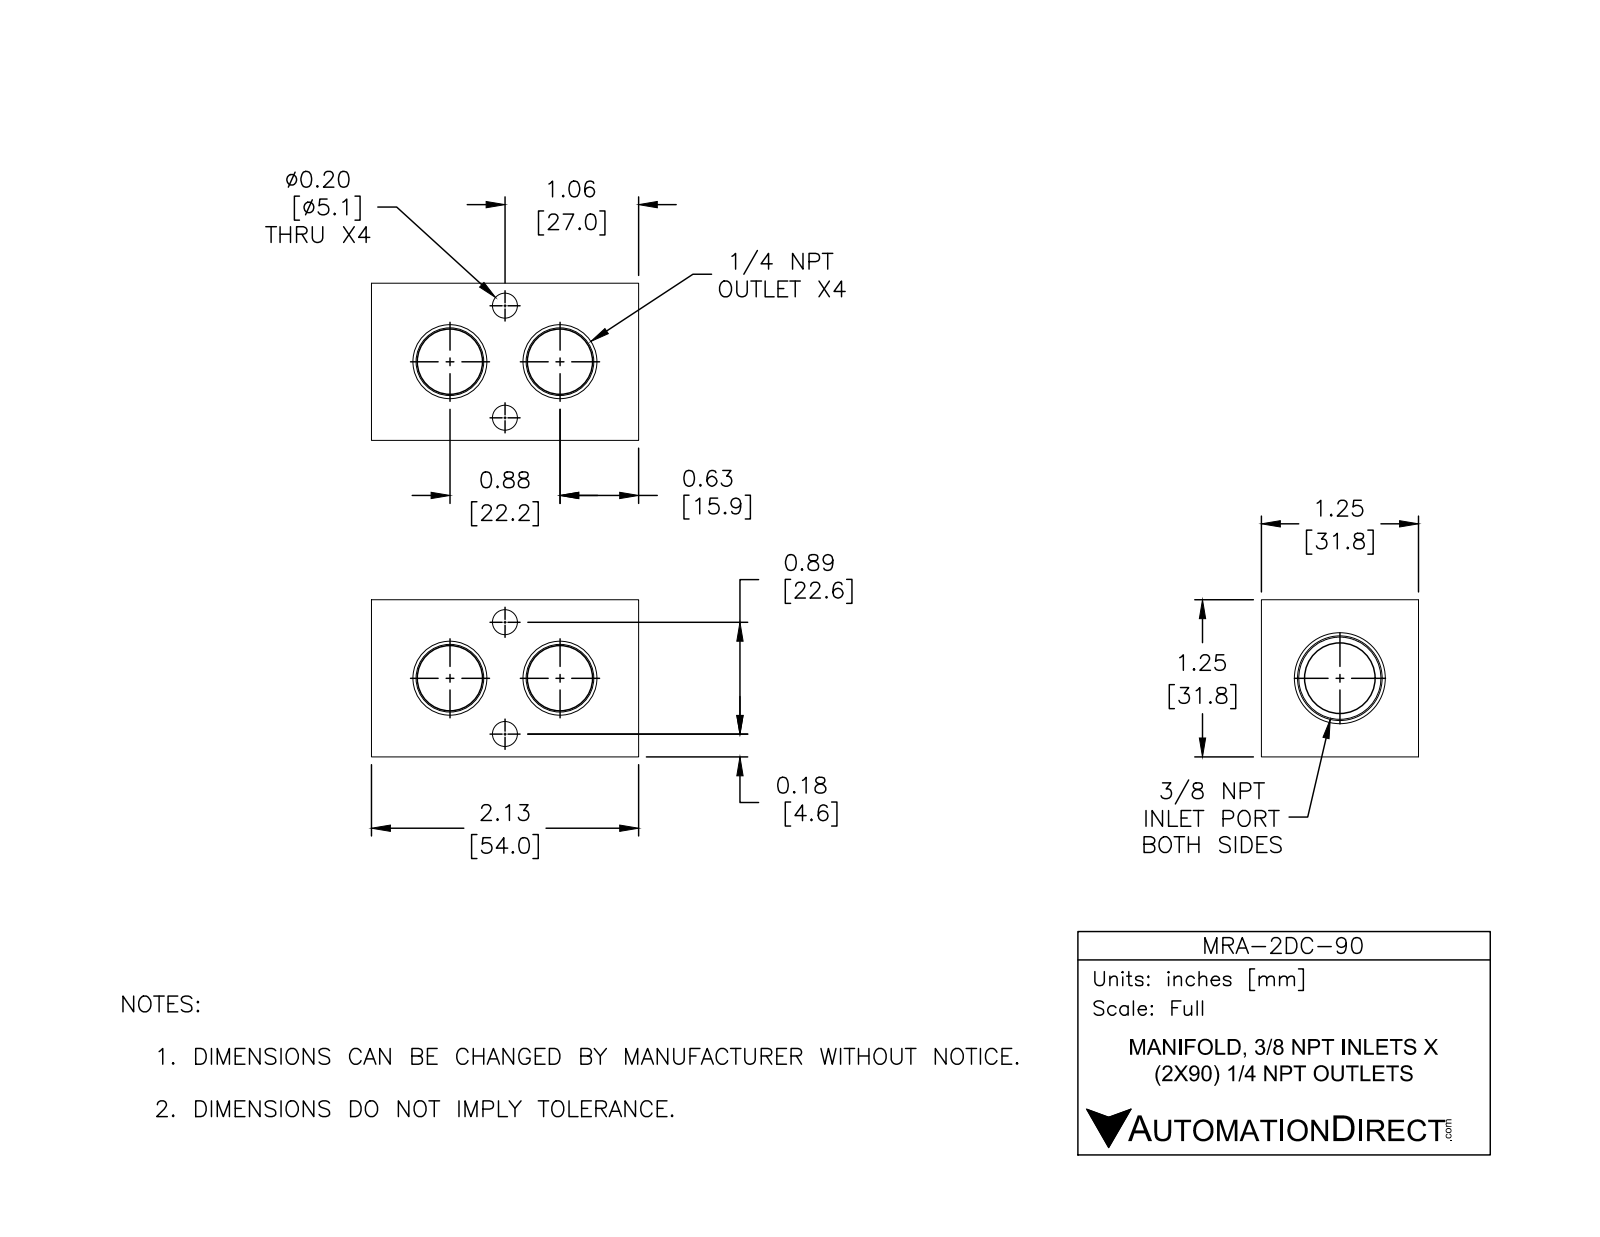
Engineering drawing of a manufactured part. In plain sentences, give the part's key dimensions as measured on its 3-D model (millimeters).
The part is named "MRA-2DC-90". Its 3-D file was written by "SolidWorks 2015 (CONFIG_CONTROL_DESIGN)". It is 1 solid with 78 faces: 18 planar, 36 cylindrical and 24 other. Overall it measures 54 by 31.8 by 31.8 millimeters. Its volume is 36 840 cubic millimeters and its surface area 13 050 square millimeters. Round holes: 4 of diameter 5.1, 1 of diameter 14.3. Partial cylindrical surfaces (rounded edges, fillets, slot ends): 4 of radius 5.6. The main face-to-face distances are 31.8, 54, 21.8, 9.9, 10.4, 43.6, 33.1. The hole center spacings are 22.6.
